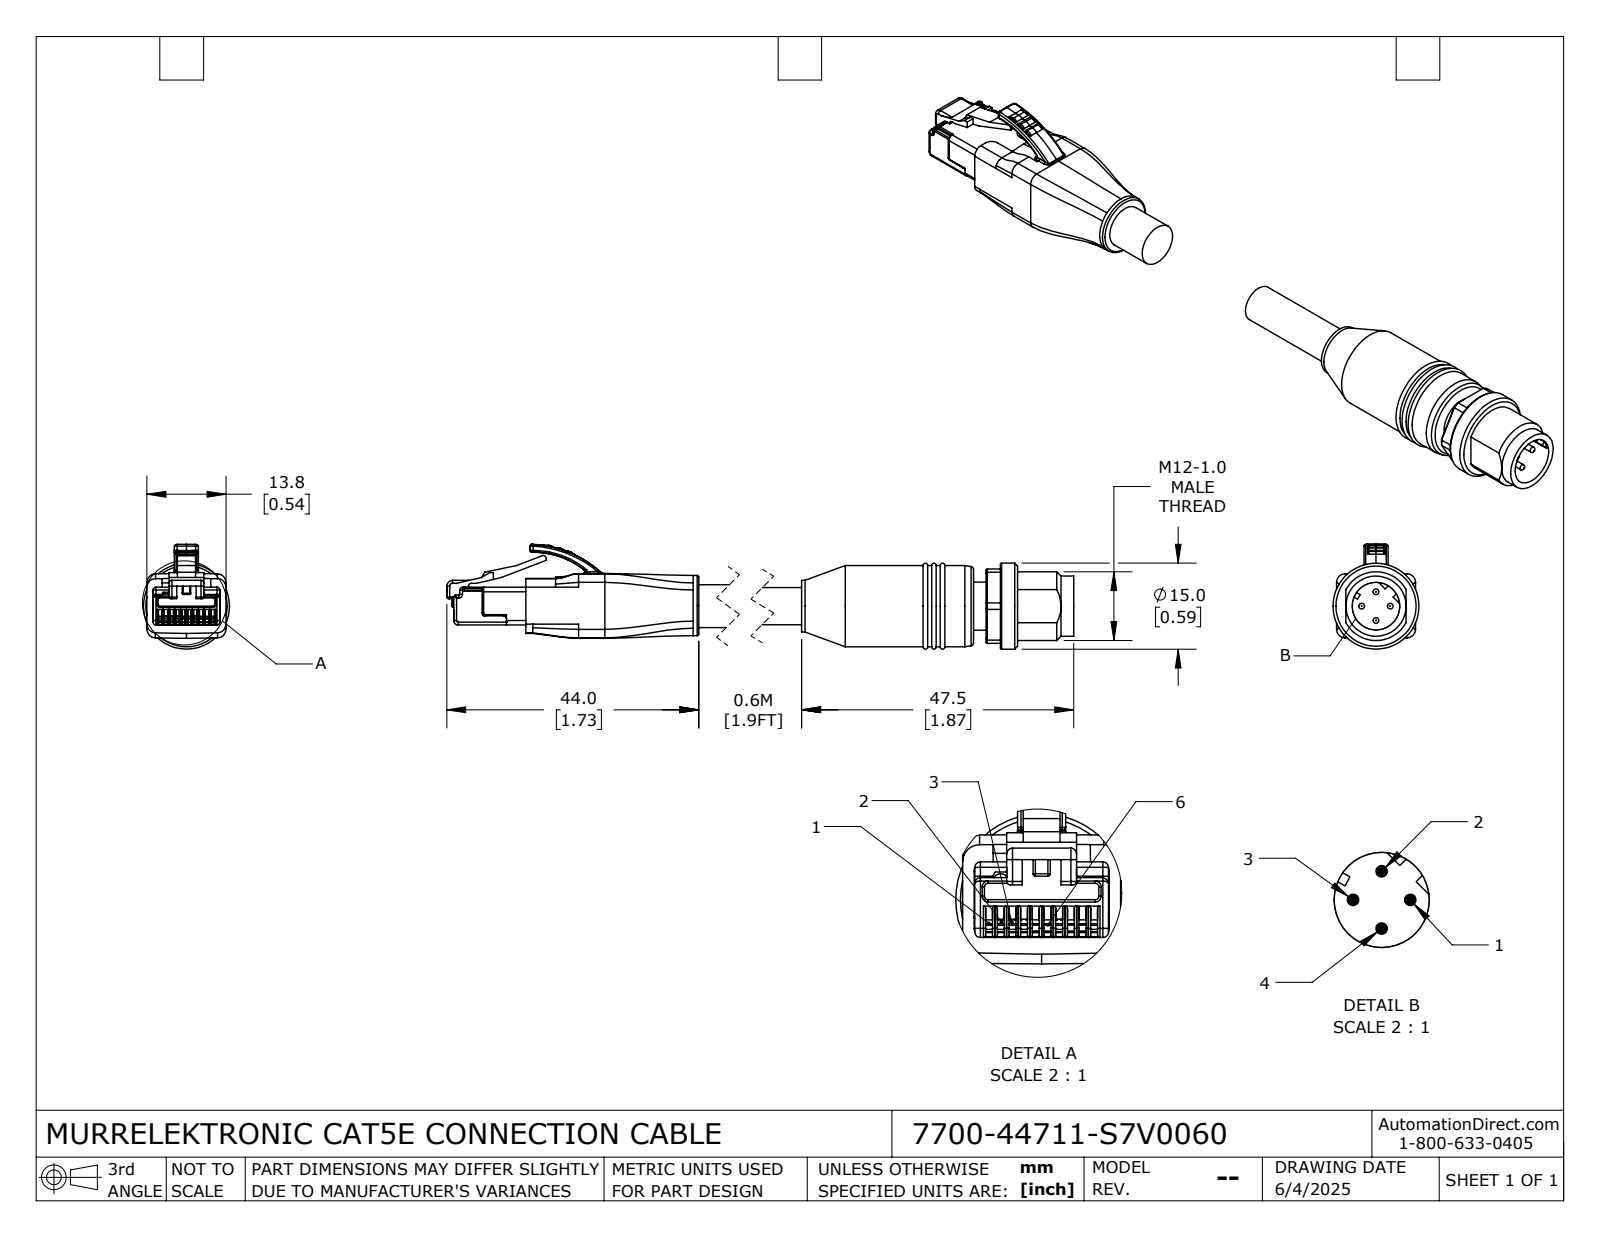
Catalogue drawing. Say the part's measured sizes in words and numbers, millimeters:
The part is named "7700-44711-S7V0060; 7700-44711-S7V0060_RJ45; 7700-44711-S7V0060_MALE". Its 3-D file was written by "SolidWorks 2024 (CONFIG_CONTROL_DESIGN)". It is 2 solids with 757 faces: 357 planar, 235 cylindrical and 165 other. Overall it measures 144.5 by 18.29 by 15 millimeters. Its volume is 11 873 cubic millimeters and its surface area 5 775 square millimeters. Round holes: 1 of diameter 8.3. Round bosses or shafts: 4 of diameter 1, 2 of diameter 10.5, 1 of diameter 15, 1 of diameter 14.2, 1 of diameter 9, 1 of diameter 8.4, 1 of diameter 7.5, 1 of diameter 6.5. Partial cylindrical surfaces (rounded edges, fillets, slot ends): 61 of radius 0.2, 25 of radius 0.5, 14 of radius 0.3, 9 of radius 1.5, 5 of radius 0.8, 2 of radius 0.54, 2 of radius 5, 1 of radius 0.13. The main face-to-face distances are 13.8, 2.2, 1.65, 12.15, 1.01, 12.79, 0.64, 11.14, 9.8, 0.9.
